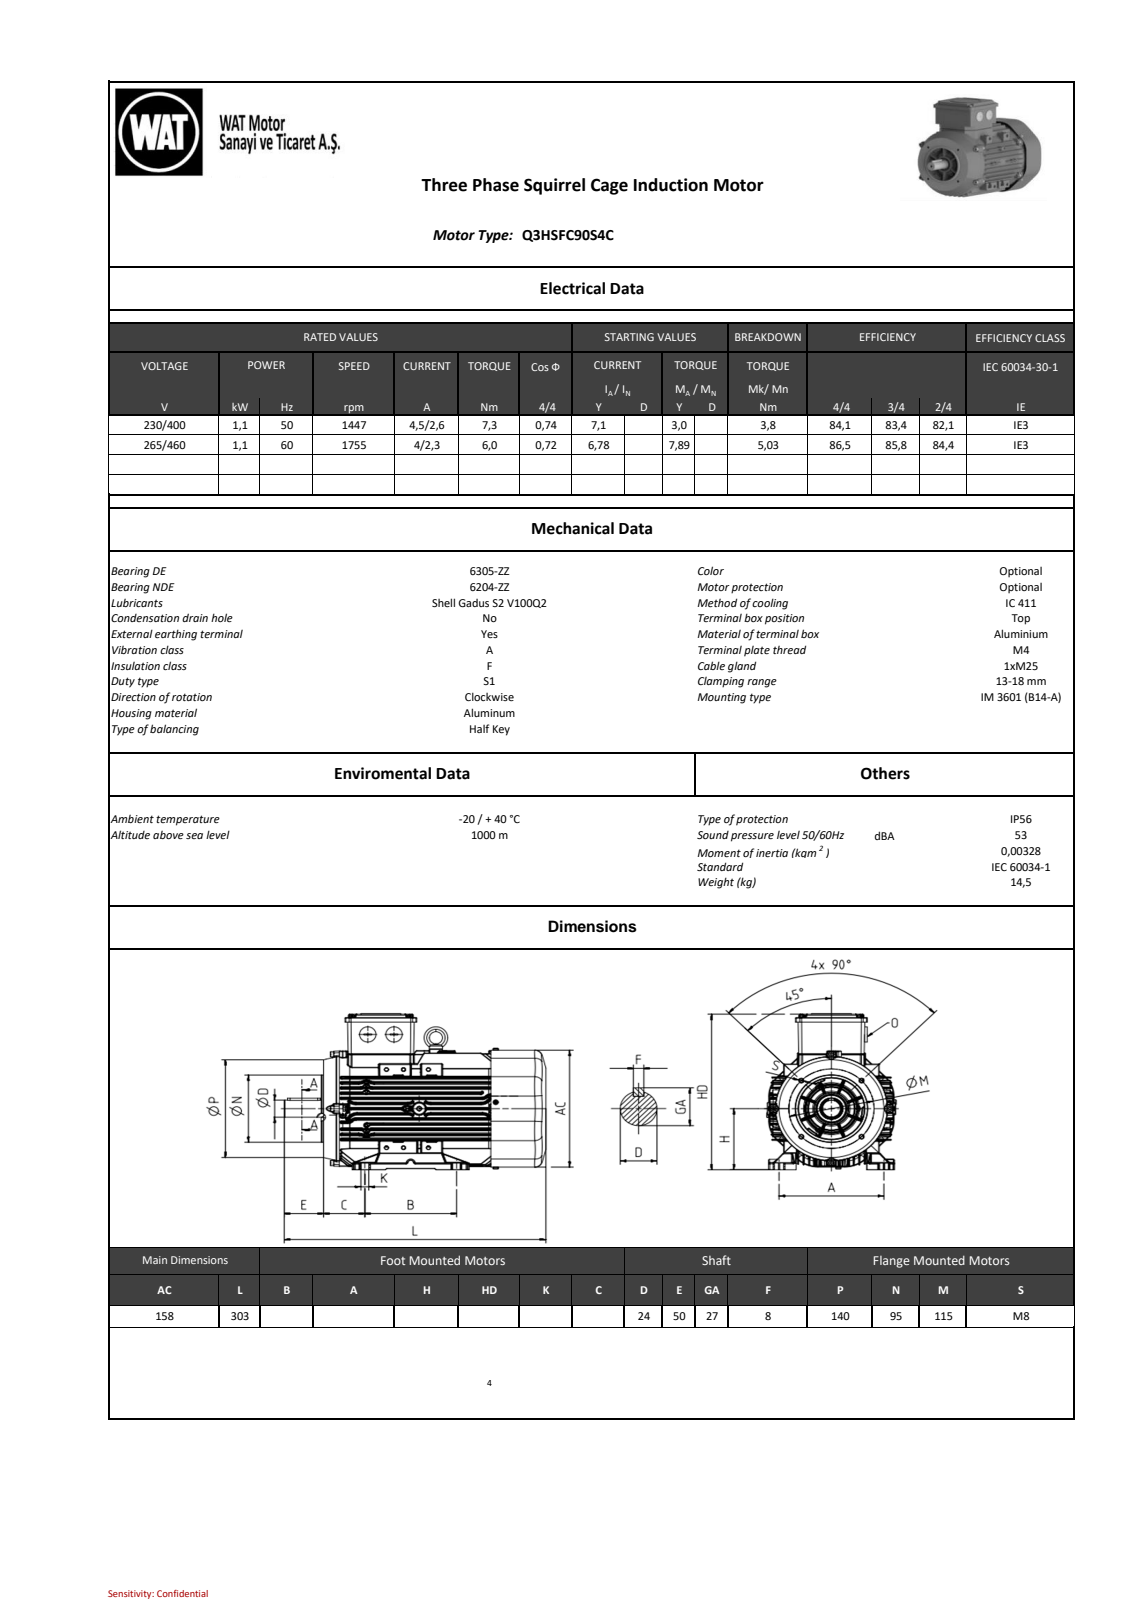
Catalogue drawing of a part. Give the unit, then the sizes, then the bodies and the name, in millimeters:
Units: millimetres
Overall size (bounding box): 303 × 200.5 × 158
Round holes (diameter × count): ⌀6.8 ×5, ⌀3 ×3, ⌀3.95 ×3, ⌀4.6 ×2, ⌀3.5 ×1, ⌀3.99 ×1, ⌀4.13 ×1, ⌀8 ×1, ⌀8.4 ×1, ⌀40 ×1, ⌀57.4 ×1
Round bosses / shafts (diameter × count): ⌀6 ×8, ⌀9.3 ×4, ⌀9.2 ×4, ⌀8.33 ×4, ⌀146.5 ×1, ⌀95 ×1, ⌀61 ×1, ⌀39.5 ×1
Partial cylindrical surfaces — rounded edges, fillets, slot ends (radius × count): R0.5 ×897, R0.8 ×333, R1 ×160, R0.75 ×22, R2 ×21, R4 ×14, R0.1 ×12, R5 ×11
Main face-to-face distances: 1, 138, 30.99, 168.99, 39.5, 41.96, 40.5, 46.5, 157, 6
Hole centre spacings: 25.5, 57.5, 81.32, 34.5, 39.18, 59.11, 59.76, 22.2
Bodies: 0 solids, 6712 faces (1285 planar, 2097 cylindrical, 3330 other)
Part name (STEP PRODUCT): Ar311A3C0609zsgg
STEP written by: SIEMENS PLM Software NX 9.0 (AUTOMOTIVE_DESIGN)
